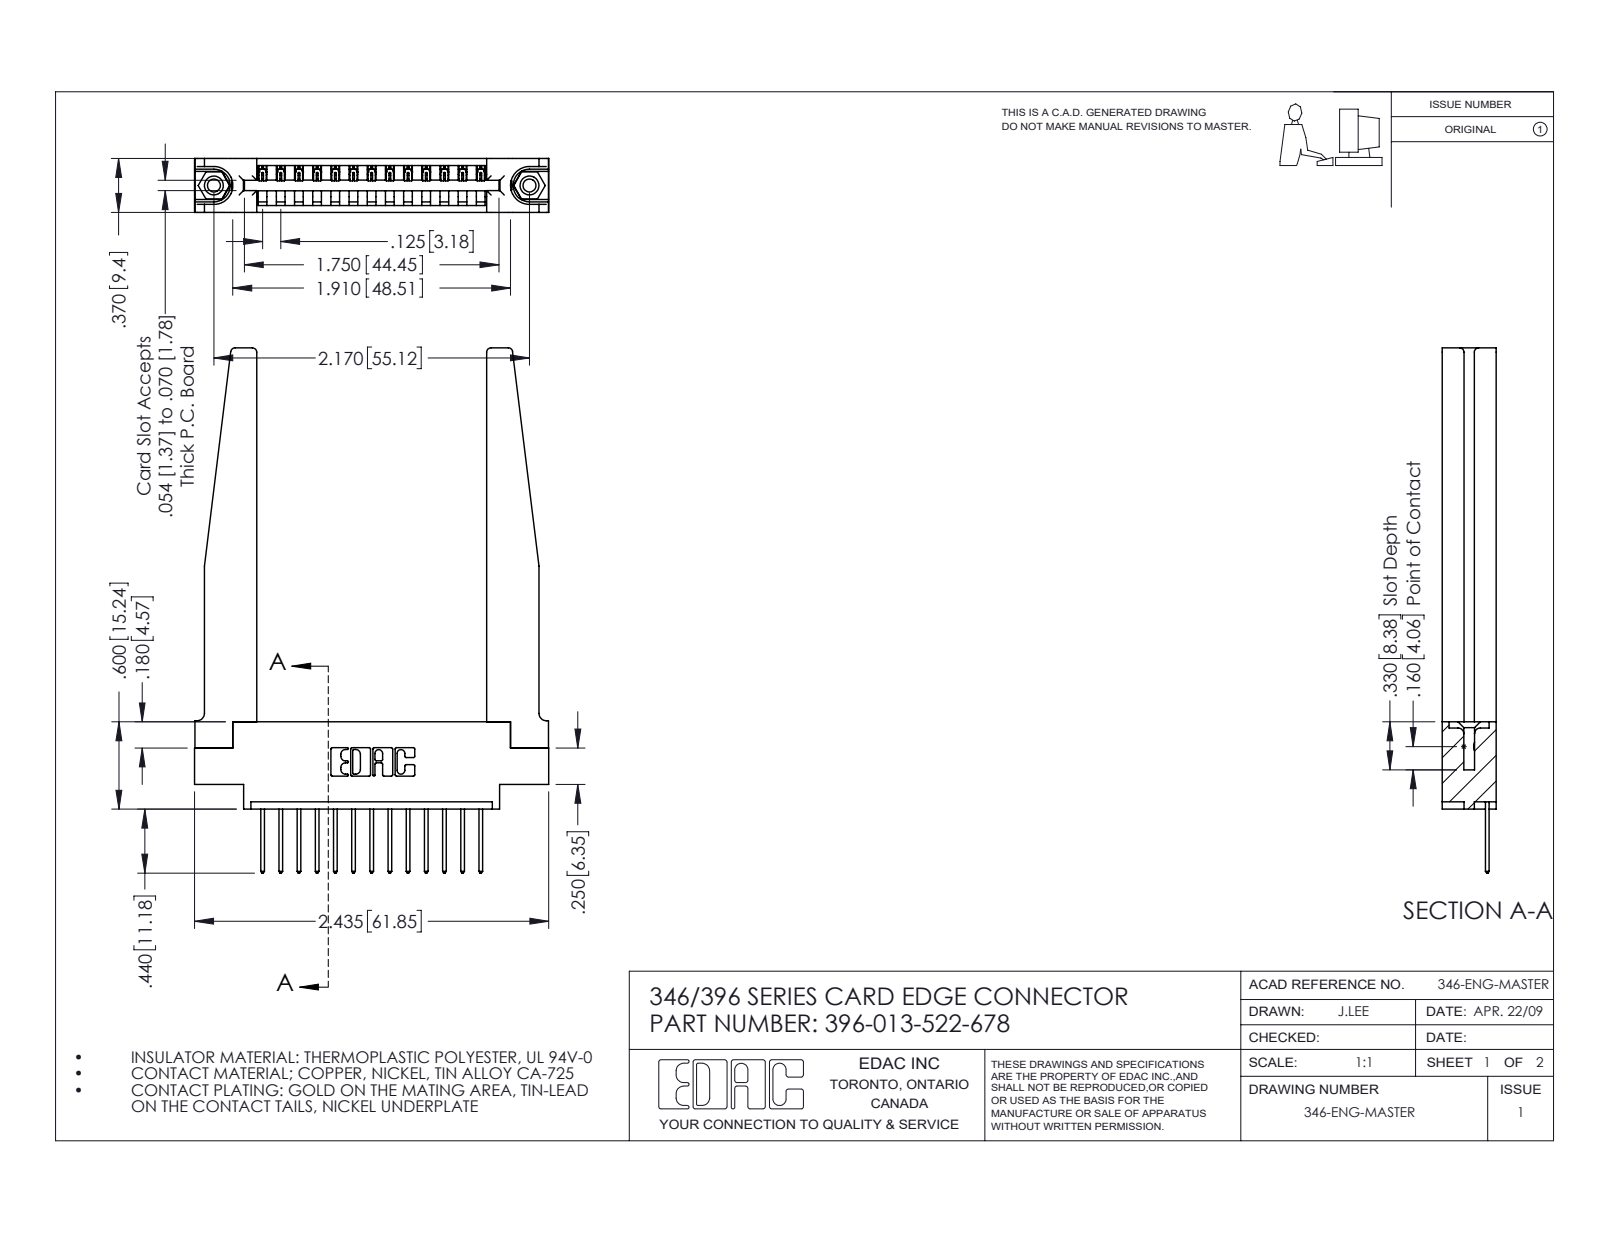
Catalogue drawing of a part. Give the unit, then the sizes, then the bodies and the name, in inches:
Units: inches
Overall size (bounding box): 3.61 × 2.435 × 0.37
Round holes (diameter × count): ⌀0.089 ×2, ⌀0.125 ×2, ⌀0.156 ×2, ⌀0.064 ×1
Round bosses / shafts (diameter × count): ⌀0.155 ×2
Partial cylindrical surfaces — rounded edges, fillets, slot ends (radius × count): R0.006 ×26, R0.01 ×26, R0.01 ×22, R0.03 ×8, R0.007 ×6, R0.031 ×6, R0.026 ×3, R0.031 ×2
Main face-to-face distances: 0.37, 0.15, 0.072, 0.148, 0.048, 0.322, 0.25, 0.102, 0.22, 0.173
Hole centre spacings: 0.246, 1.964, 2.17
Volume: 0.761 in³ · Surface area: 20.76 in²
Bodies: 18 solids, 1114 faces (742 planar, 320 cylindrical, 52 other)
Part name (STEP PRODUCT): 346 Part_0.170 Offset - 0.156 Dia-TH; 345-292-001_345-293-122; 346-220-078_345-220-078; 345-250-001_345-250-001-102 (+1 more)
STEP written by: SolidWorks 2016 (CONFIG_CONTROL_DESIGN)
